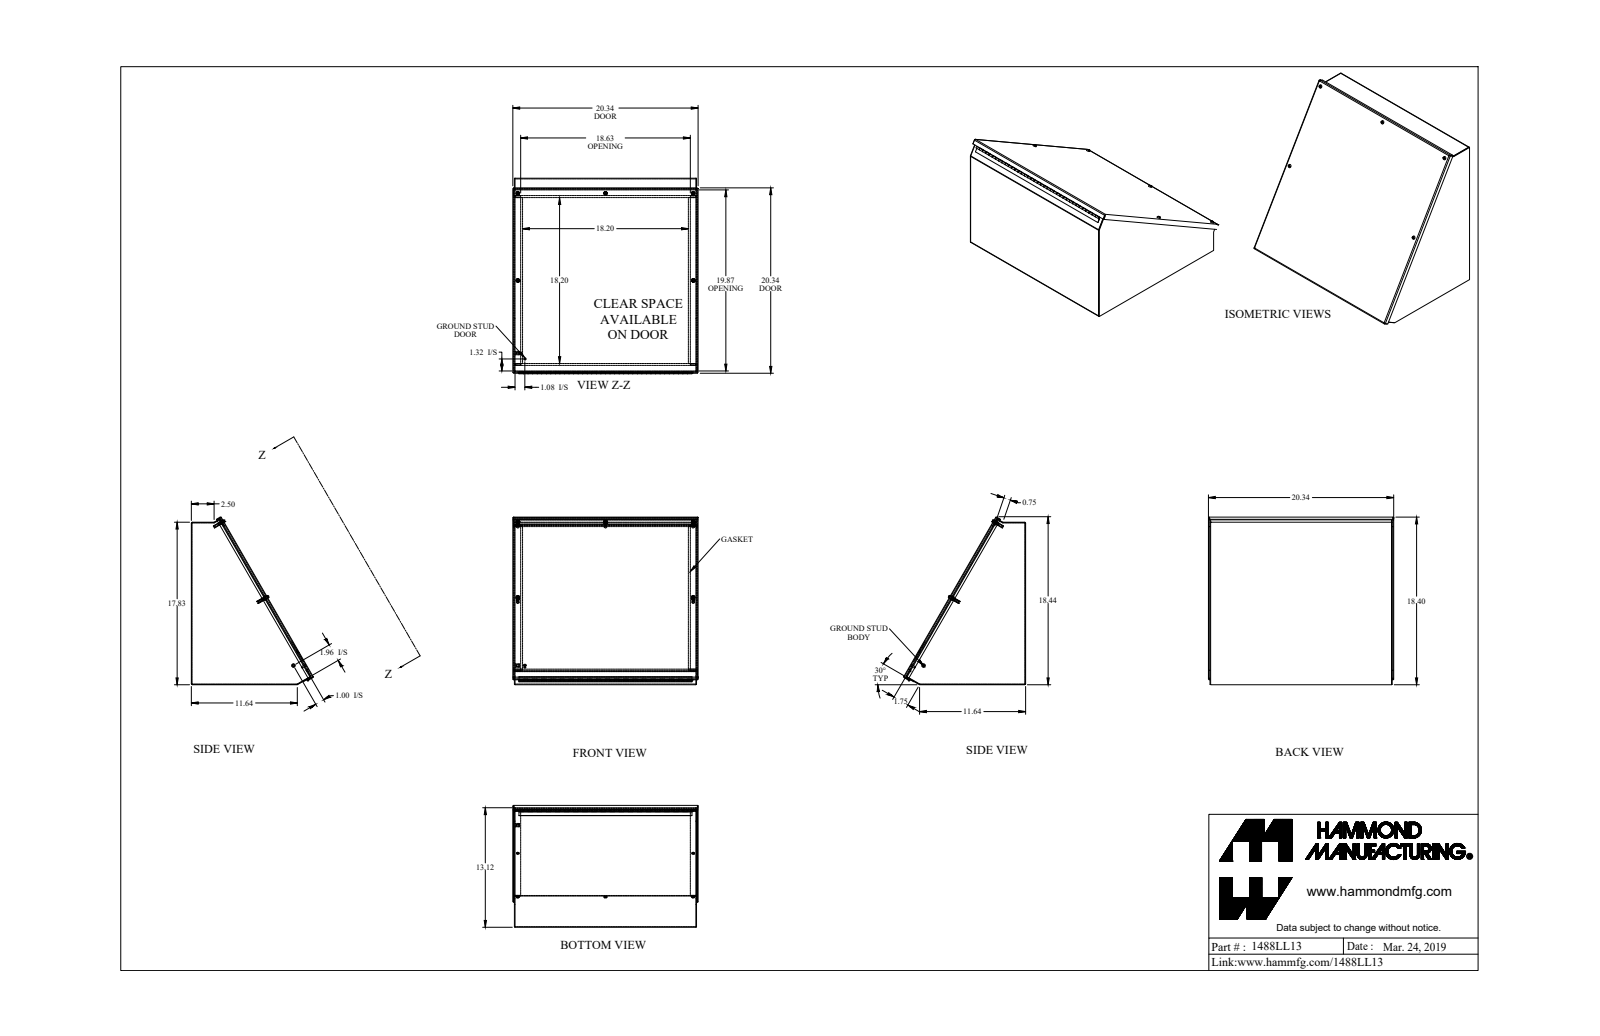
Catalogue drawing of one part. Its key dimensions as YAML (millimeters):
part_name: "1488LL13_Default"
step_written_by: "SolidWorks 2019 (CONFIG_CONTROL_DESIGN)"
units: millimeters
bodies: {solids: 26, faces: 829, planar: 542, cylindrical: 239, other: 48}
overall_size: [516.7, 467.3, 339.7]
volume: 2081000
surface_area: 2088000
round_holes:
  - {diameter: 4, count: 5}
  - {diameter: 6.4, count: 5}
  - {diameter: 4, count: 1}
round_bosses_or_shafts:
  - {diameter: 9.9, count: 5}
  - {diameter: 7, count: 5}
  - {diameter: 4.8, count: 5}
  - {diameter: 3.8, count: 5}
  - {diameter: 9.5, count: 1}
  - {diameter: 6.4, count: 1}
  - {diameter: 4.8, count: 1}
  - {diameter: 4.4, count: 1}
partial_cylinders:
  - {radius: 0.9, count: 12}
  - {radius: 2.7, count: 12}
  - {radius: 3.2, count: 5}
  - {radius: 4.1, count: 5}
  - {radius: 4.3, count: 5}
face_to_face_distances: [1.8, 506.2, 504.3, 508, 451.1, 6.4, 8.2, 5, 3.2, 3.2]
hole_center_spacings: [244.5, 489, 243.3, 243.3, 244.5, 344.8, 344.9, 489]
